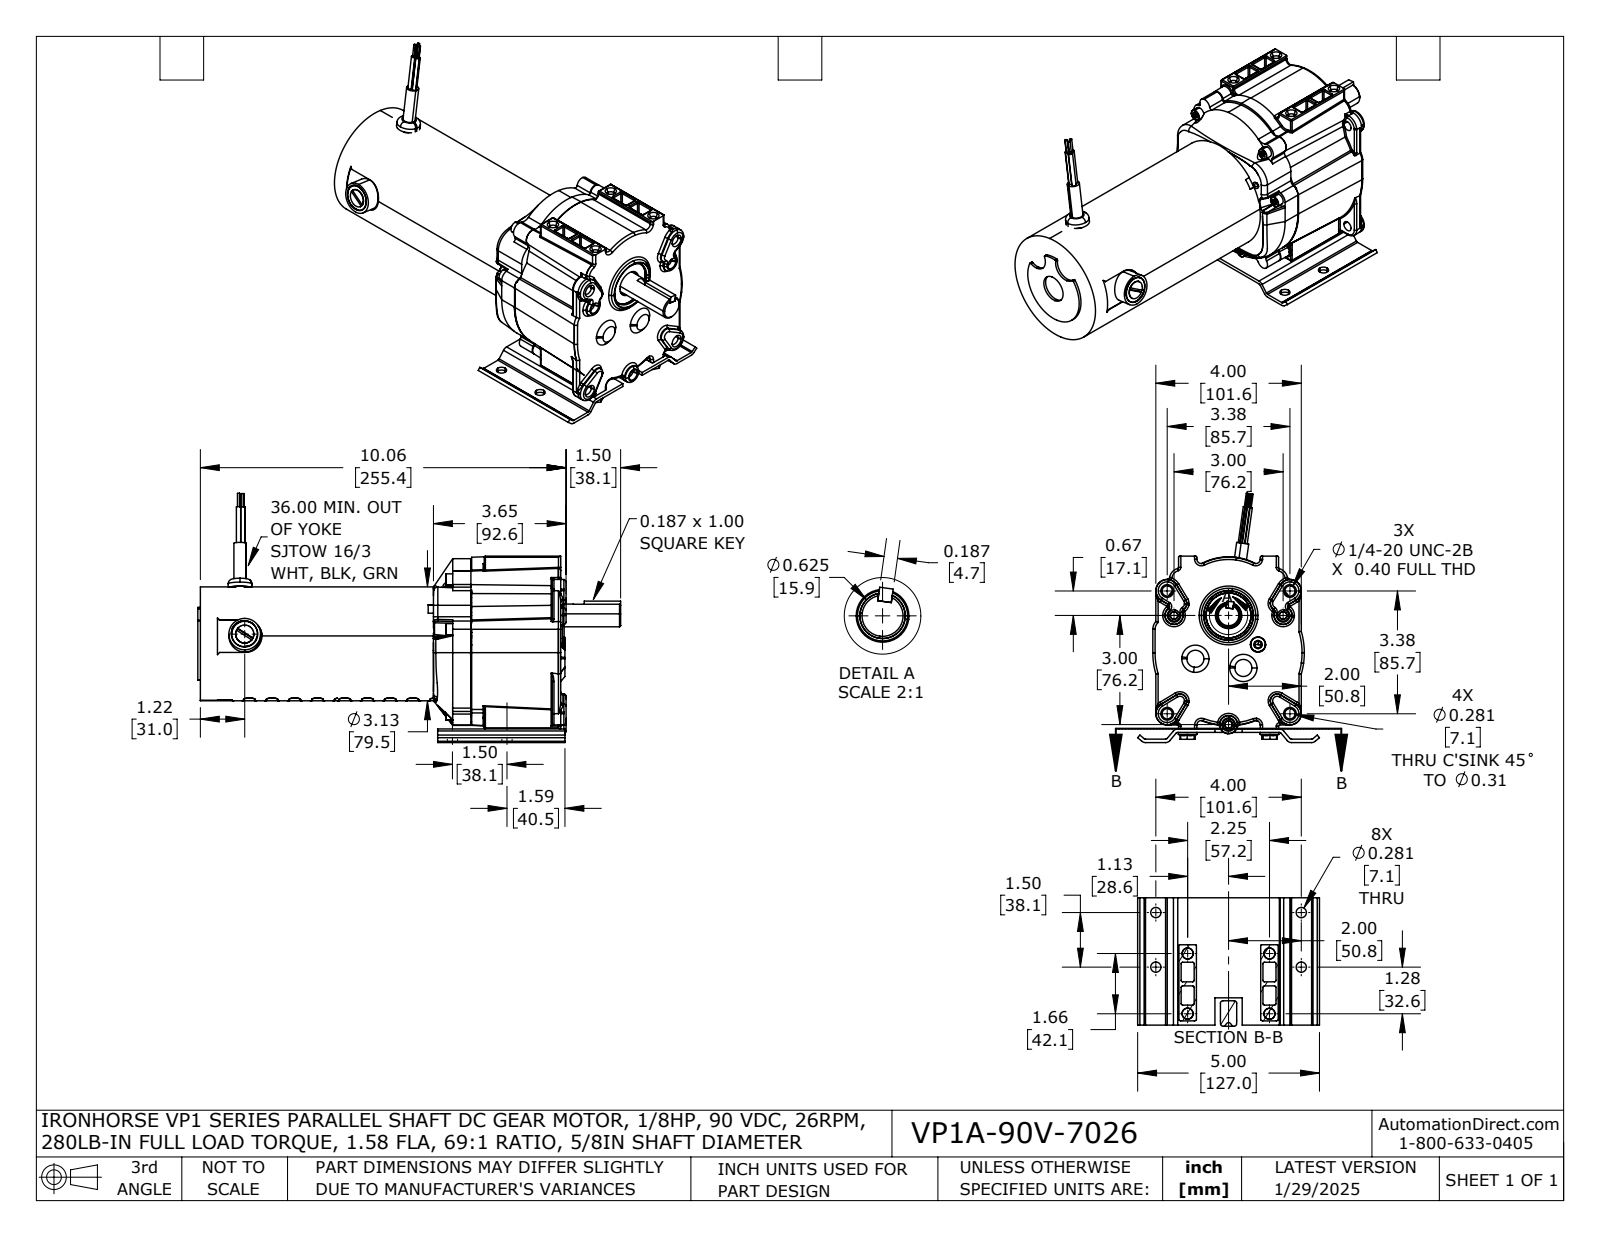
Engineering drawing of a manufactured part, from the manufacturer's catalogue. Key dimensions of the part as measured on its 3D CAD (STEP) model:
Part name (STEP PRODUCT): VP1A-90V-7026
STEP written by: SolidWorks 2024 (AUTOMOTIVE_DESIGN)
Units: inches
Bodies: 10 solids, 2472 faces (654 planar, 701 cylindrical, 1117 other)
Overall size (bounding box): 11.627 × 6.854 × 5
Volume: 98.93 in³ · Surface area: 345.4 in²
Round holes (diameter × count): ⌀0.281 ×12, ⌀0.218 ×5, ⌀0.159 ×3, ⌀0.207 ×3, ⌀0.135 ×2, ⌀0.166 ×2, ⌀0.204 ×2, ⌀0.397 ×2, ⌀0.688 ×2, ⌀0.875 ×2, ⌀0.75 ×1, ⌀0.813 ×1
Round bosses / shafts (diameter × count): ⌀0.307 ×5, ⌀0.19 ×5, ⌀0.51 ×4, ⌀0.3 ×4, ⌀0.12 ×3, ⌀0.06 ×3, ⌀0.873 ×2, ⌀0.733 ×2
Partial cylindrical surfaces — rounded edges, fillets, slot ends (radius × count): R0.03 ×52, R0.031 ×38, R0.062 ×23, R0.12 ×18, R0.156 ×18, R0.19 ×10, R0.151 ×9, R0.161 ×9
Main face-to-face distances: 0.095, 2.449, 3.5, 1.051, 9.44, 6.991, 5.94, 0.47, 6.97, 9.91
Hole centre spacings: 1.5, 3.375, 1.691, 0.492, 0.698, 1.224, 1.426, 1.552
